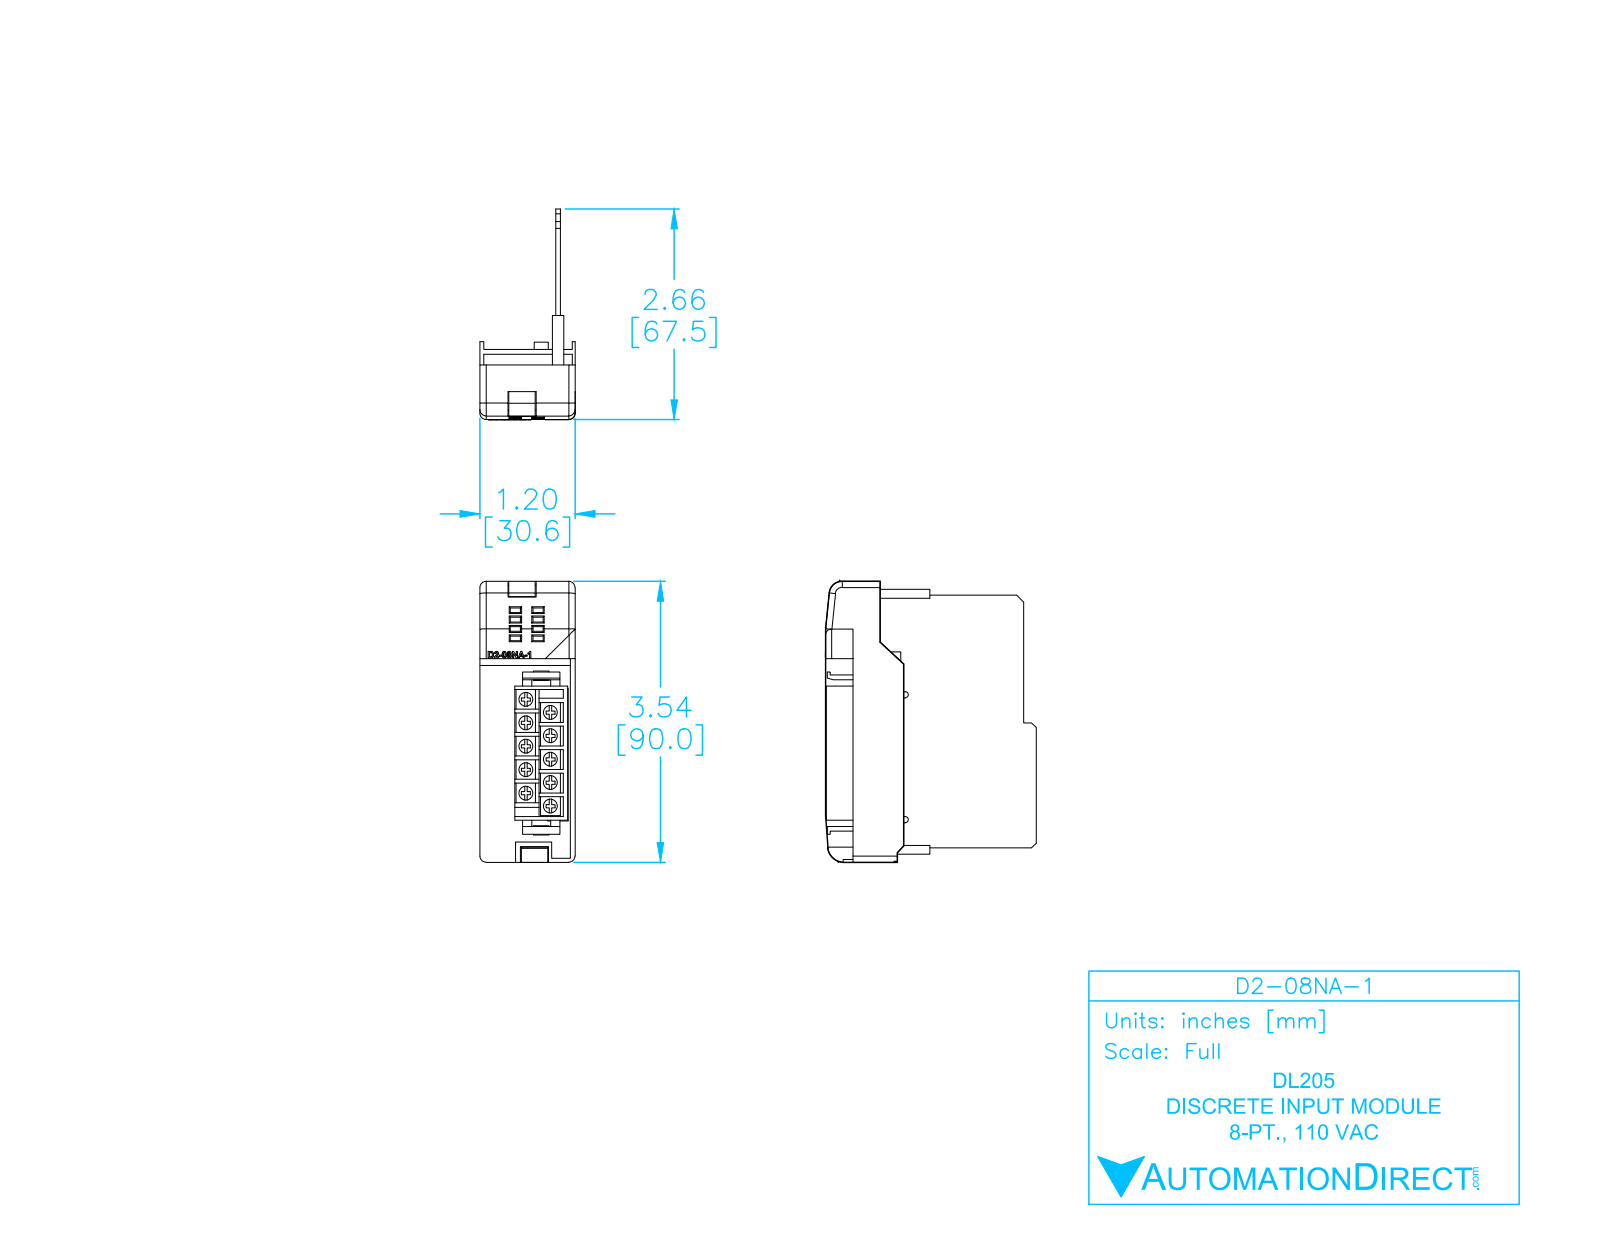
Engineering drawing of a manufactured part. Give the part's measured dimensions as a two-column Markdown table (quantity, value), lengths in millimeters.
| quantity | value |
| --- | --- |
| part name | D2-08NA-1_ModuleCase_light_NEW |
| STEP written by | SolidWorks 2009 (AUTOMOTIVE_DESIGN) |
| units | millimeters |
| bodies | 6 solids, 580 faces (412 planar, 75 cylindrical, 93 other) |
| overall size | 90 × 67.56 × 30.55 |
| volume | 25 372 mm³ |
| surface area | 28 530 mm² |
| round bosses / shafts (diameter × count) | 4.5 × 10 |
| partial cylindrical surfaces (radius × count) | 0.35 × 16, 2 × 9, 0.25 × 2, 1 × 2, 1.25 × 2, 4.12 × 1, 5.39 × 1 |
| main face-to-face distances | 1.5, 4.72, 6.22, 2.37, 3.87, 2.35, 3.22, 0.85, 8.14, 24.28 |
